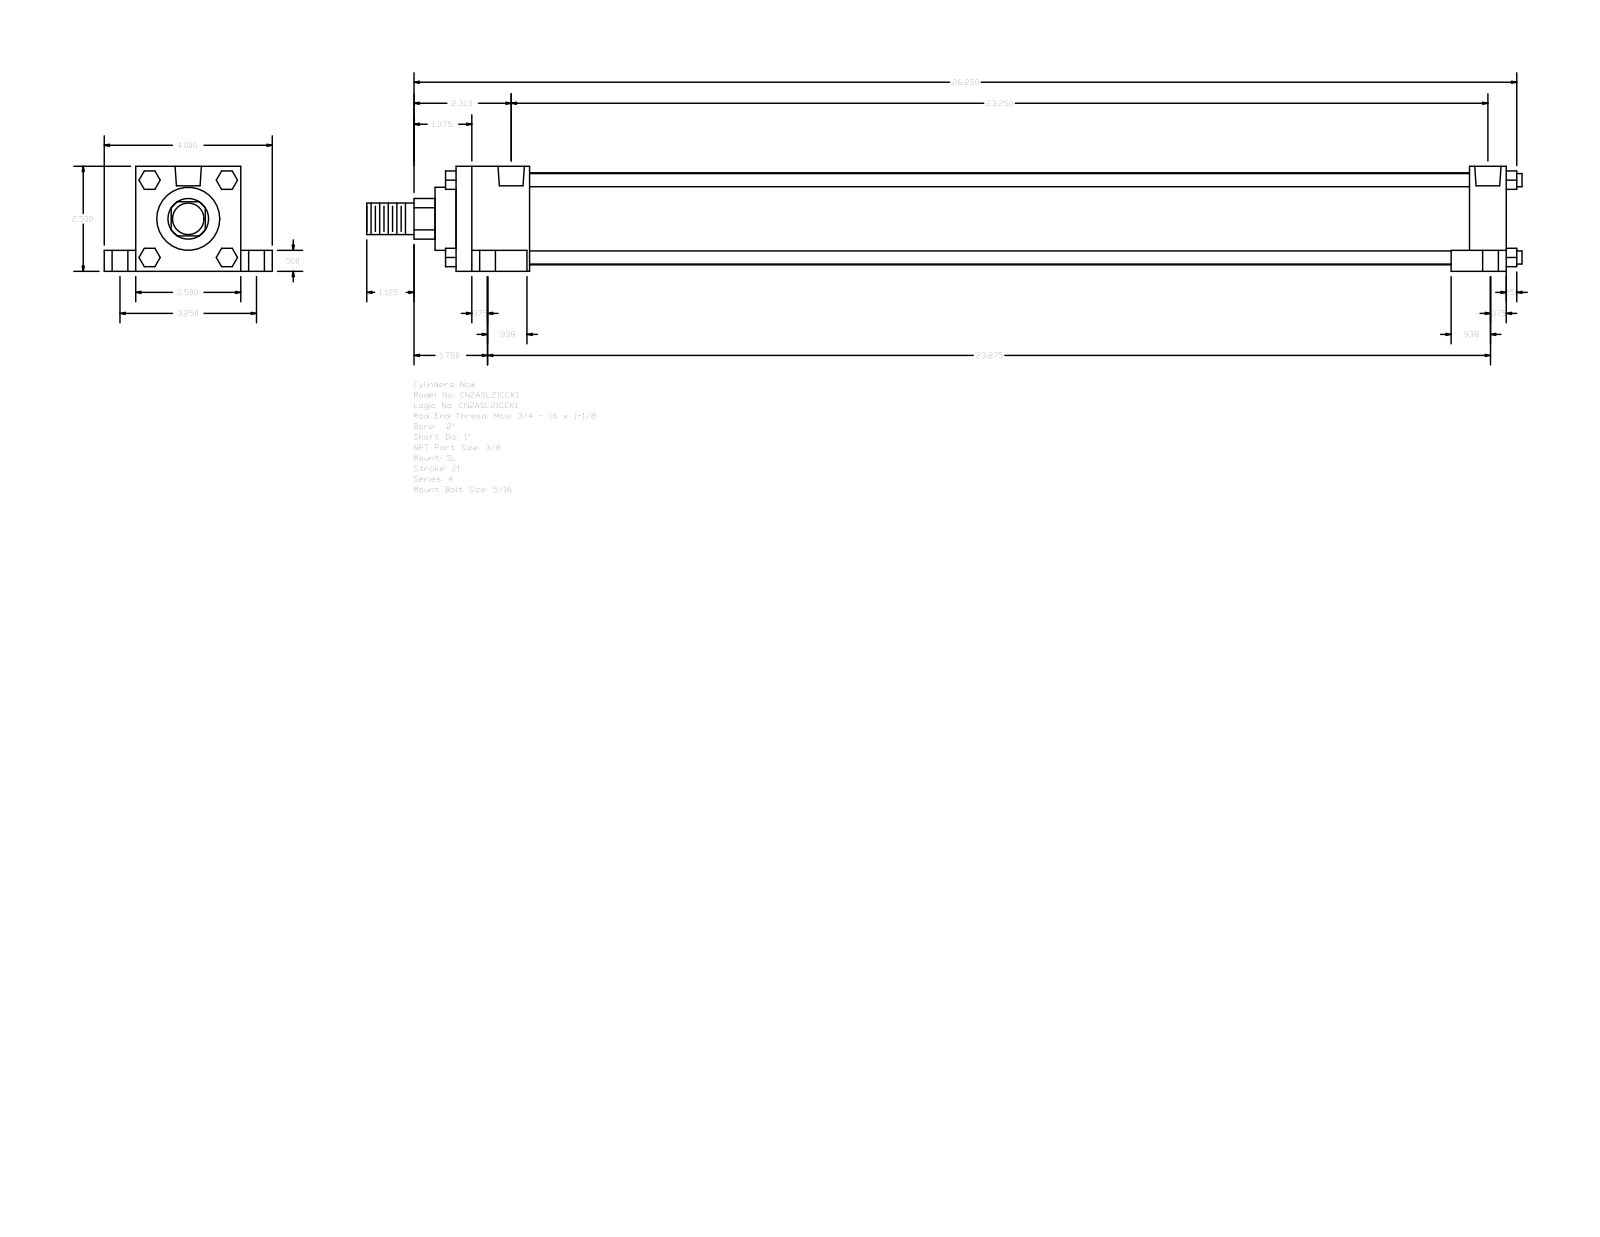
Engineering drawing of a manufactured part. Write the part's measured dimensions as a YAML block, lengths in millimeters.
part_name: "A_SL__0200_1"
step_written_by: "GSSL Pune (CONFIG_CONTROL_DESIGN)"
units: millimeters
bodies: {solids: 0, faces: 148, planar: 112, cylindrical: 36, other: 0}
overall_size: [698.5, 101.6, 63.5]
round_holes:
  - {diameter: 5.56, count: 4}
  - {diameter: 9.53, count: 4}
  - {diameter: 15.88, count: 4}
  - {diameter: 15.93, count: 2}
round_bosses_or_shafts:
  - {diameter: 7.94, count: 4}
  - {diameter: 55.63, count: 1}
  - {diameter: 38.1, count: 1}
  - {diameter: 25.4, count: 1}
  - {diameter: 19.05, count: 1}
partial_cylinders:
  - {radius: 12.29, count: 1}
face_to_face_distances: [63.5, 635, 12.7, 50.8, 19.05, 82.55, 44.45, 590.55, 612.77, 568.32]
hole_center_spacings: [41.3, 41.64, 43.67, 44.22, 82.54, 584.98, 591.99, 593.58]
